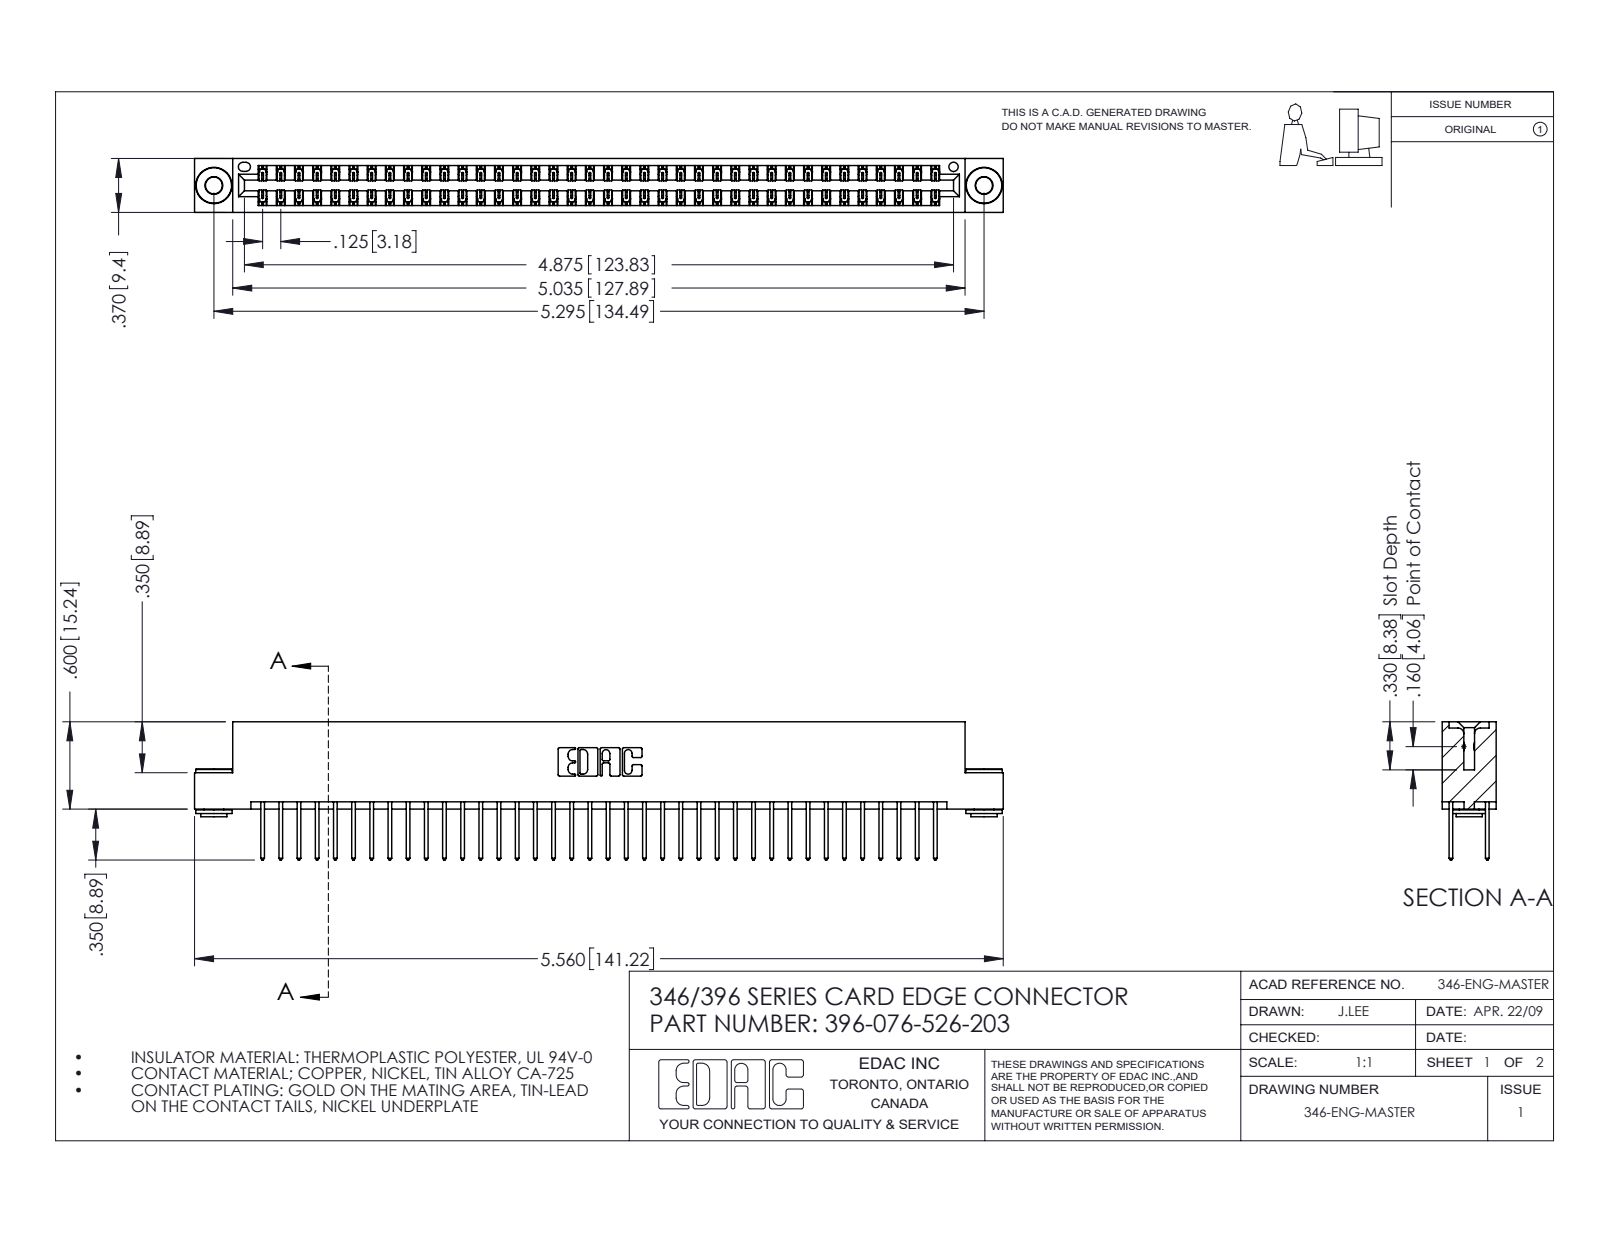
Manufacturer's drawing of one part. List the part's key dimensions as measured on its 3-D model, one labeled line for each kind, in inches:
Part name (STEP PRODUCT): 345-292-001_345-293-126; 345-250-002_345-250-002-102; 346 Part_Flush Mounting Lugs - 0.156 Dia-TH; 396-076-526-203
STEP written by: SolidWorks 2016 (CONFIG_CONTROL_DESIGN)
Units: inches
Bodies: 79 solids, 4112 faces (2746 planar, 1358 cylindrical, 8 other)
Overall size (bounding box): 5.56 × 0.95 × 0.37
Volume: 0.847 in³ · Surface area: 30.68 in²
Round holes (diameter × count): ⌀0.116 ×2, ⌀0.156 ×2, ⌀0.064 ×1
Round bosses / shafts (diameter × count): ⌀0.25 ×2, ⌀0.18 ×2, ⌀0.136 ×2
Partial cylindrical surfaces — rounded edges, fillets, slot ends (radius × count): R0.006 ×114, R0.01 ×76, R0.01 ×22, R0.007 ×6, R0.031 ×6, R0.026 ×3, R0.014 ×2, R0.022 ×2
Main face-to-face distances: 0.048, 0.322, 0.25, 0.37, 0.025, 0.072, 0.298, 0.275, 0.148, 0.222
Hole centre spacings: 0.246, 5.086, 5.295
